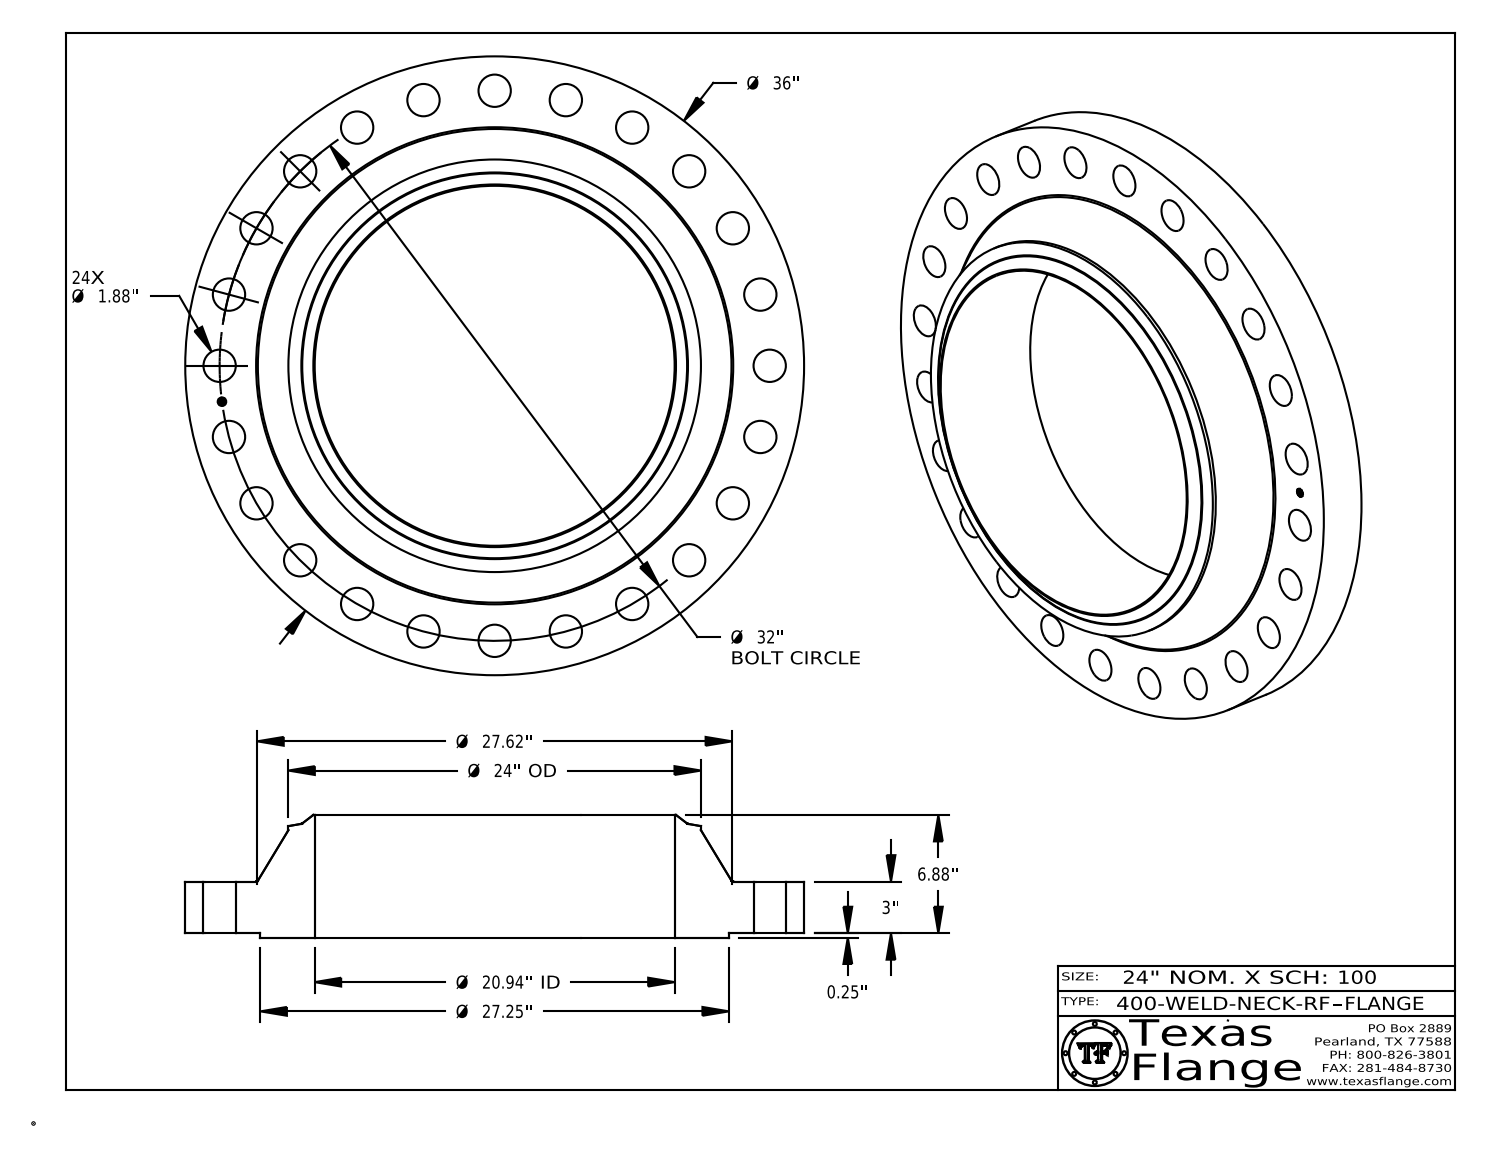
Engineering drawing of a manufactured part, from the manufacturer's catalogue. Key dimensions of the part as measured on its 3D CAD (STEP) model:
Part name (STEP PRODUCT): 400-WELD-NECK-RF
STEP written by: CATIA V5 STEP AP214 (AUTOMOTIVE_DESIGN)
Units: inches
Bodies: 1 solid, 455 faces (369 planar, 76 cylindrical, 10 other)
Overall size (bounding box): 36 × 36 × 7.13
Volume: 2 469 in³ · Surface area: 2 635 in²
Round holes (diameter × count): ⌀1.88 ×24, ⌀0.495 ×1, ⌀20.938 ×1
Round bosses / shafts (diameter × count): ⌀0.03 ×8, ⌀36 ×1, ⌀27.25 ×1, ⌀24 ×1, ⌀0.39 ×1
Main face-to-face distances: 3, 0.25, 3.25, 7.13, 6.88, 3.88, 3.235, 2.985, 0.015, 3.895
Hole centre spacings: 16, 30.909, 4.177, 8.282, 12.246, 19.48, 22.627, 25.387
